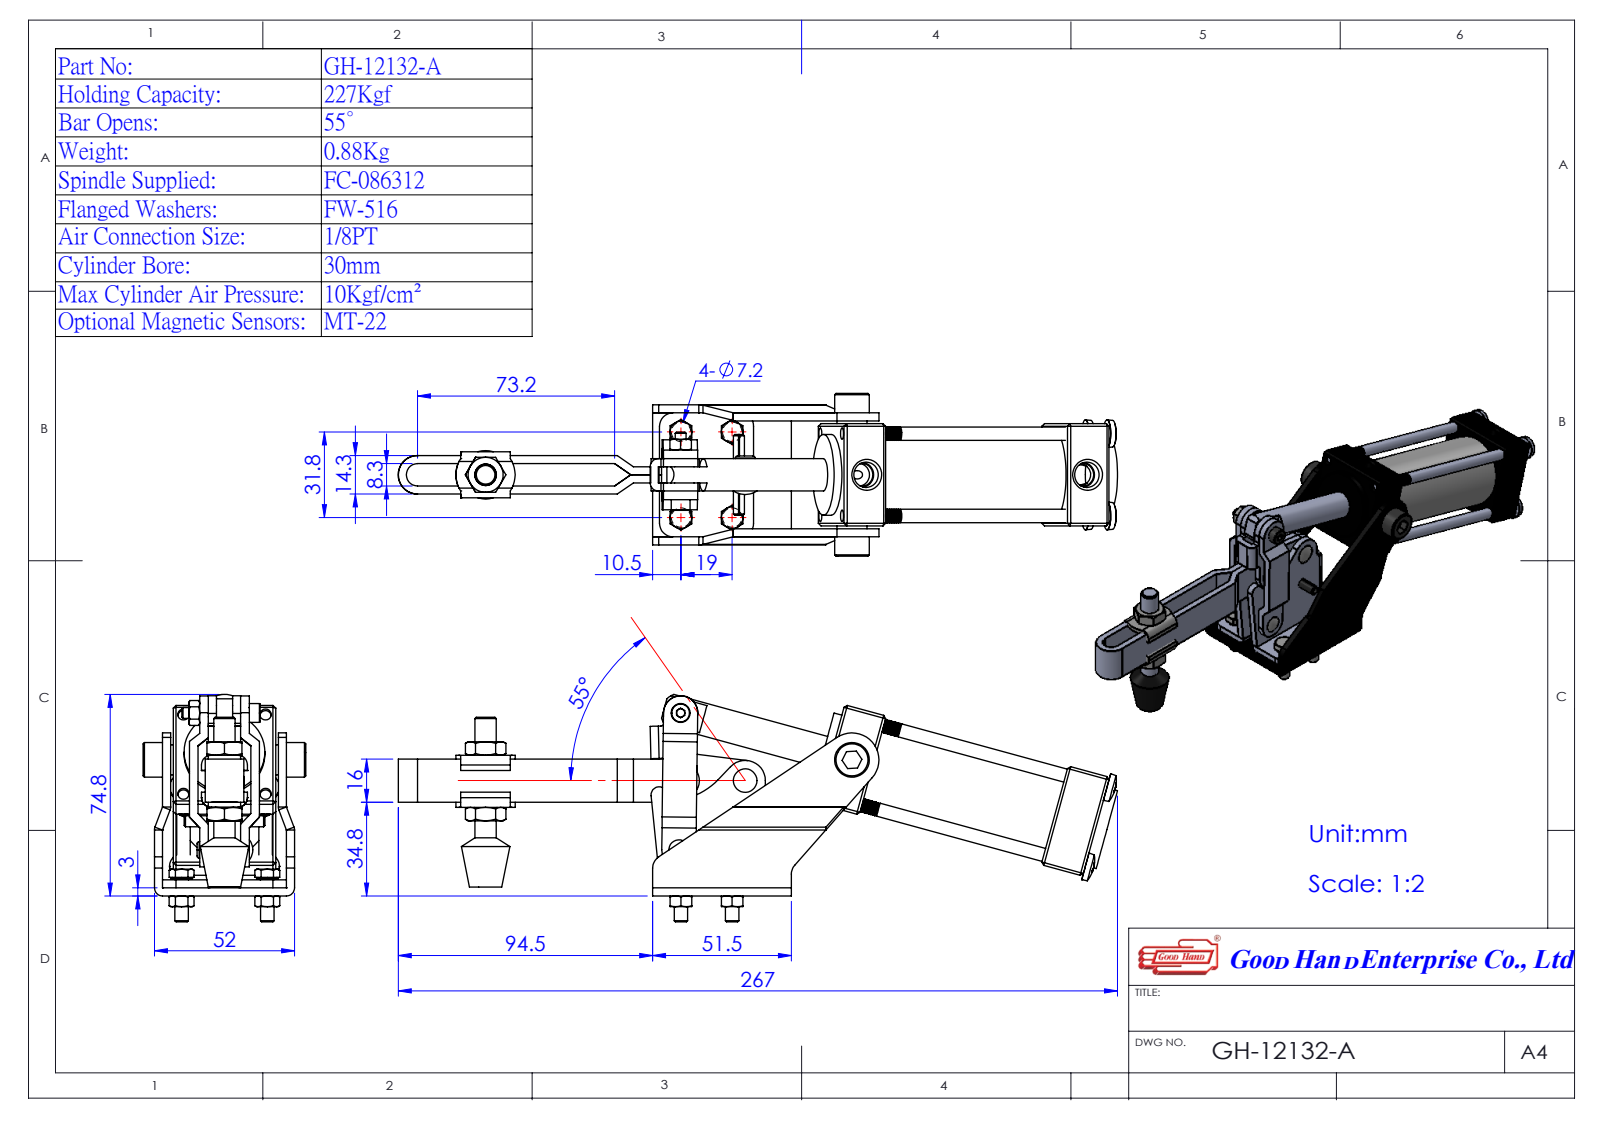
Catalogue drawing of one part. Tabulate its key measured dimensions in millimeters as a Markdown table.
| quantity | value |
| --- | --- |
| part name | GH-12132-A(簡化); Group2^GH-12132-A(簡化); 12130A-CYLINDER-1^GH-12132-A(簡化); 12130A氣缸-1^GH-12132-A(簡化) (+4 more) |
| STEP written by | SolidWorks 2016 (AUTOMOTIVE_DESIGN) |
| units | millimeters |
| bodies | 7 solids, 1023 faces (444 planar, 273 cylindrical, 306 other) |
| overall size | 267.03 × 88.79 × 62 |
| volume | 157 104 mm³ |
| surface area | 87 110 mm² |
| round holes (diameter × count) | 4 × 2, 5.5 × 2, 7.9 × 2, 6 × 1, 8 × 1, 12 × 1, 30 × 1 |
| round bosses / shafts (diameter × count) | 6 × 5, 10.3 × 4, 10 × 4, 5 × 4, 30 × 3, 9 × 2, 6.35 × 2, 6.3 × 2 |
| partial cylindrical surfaces (radius × count) | 3 × 8, 3.01 × 6, 5 × 6, 1.2 × 4, 3.6 × 4, 7.5 × 4, 1 × 2, 6.35 × 2 |
| main face-to-face distances | 3, 6, 26, 23, 20, 29, 17, 1.15, 4.15, 7.15 |
| hole center spacings | 23.4, 25.1, 25.73, 34.69, 35.58, 40.39, 50.79, 63.52 |
